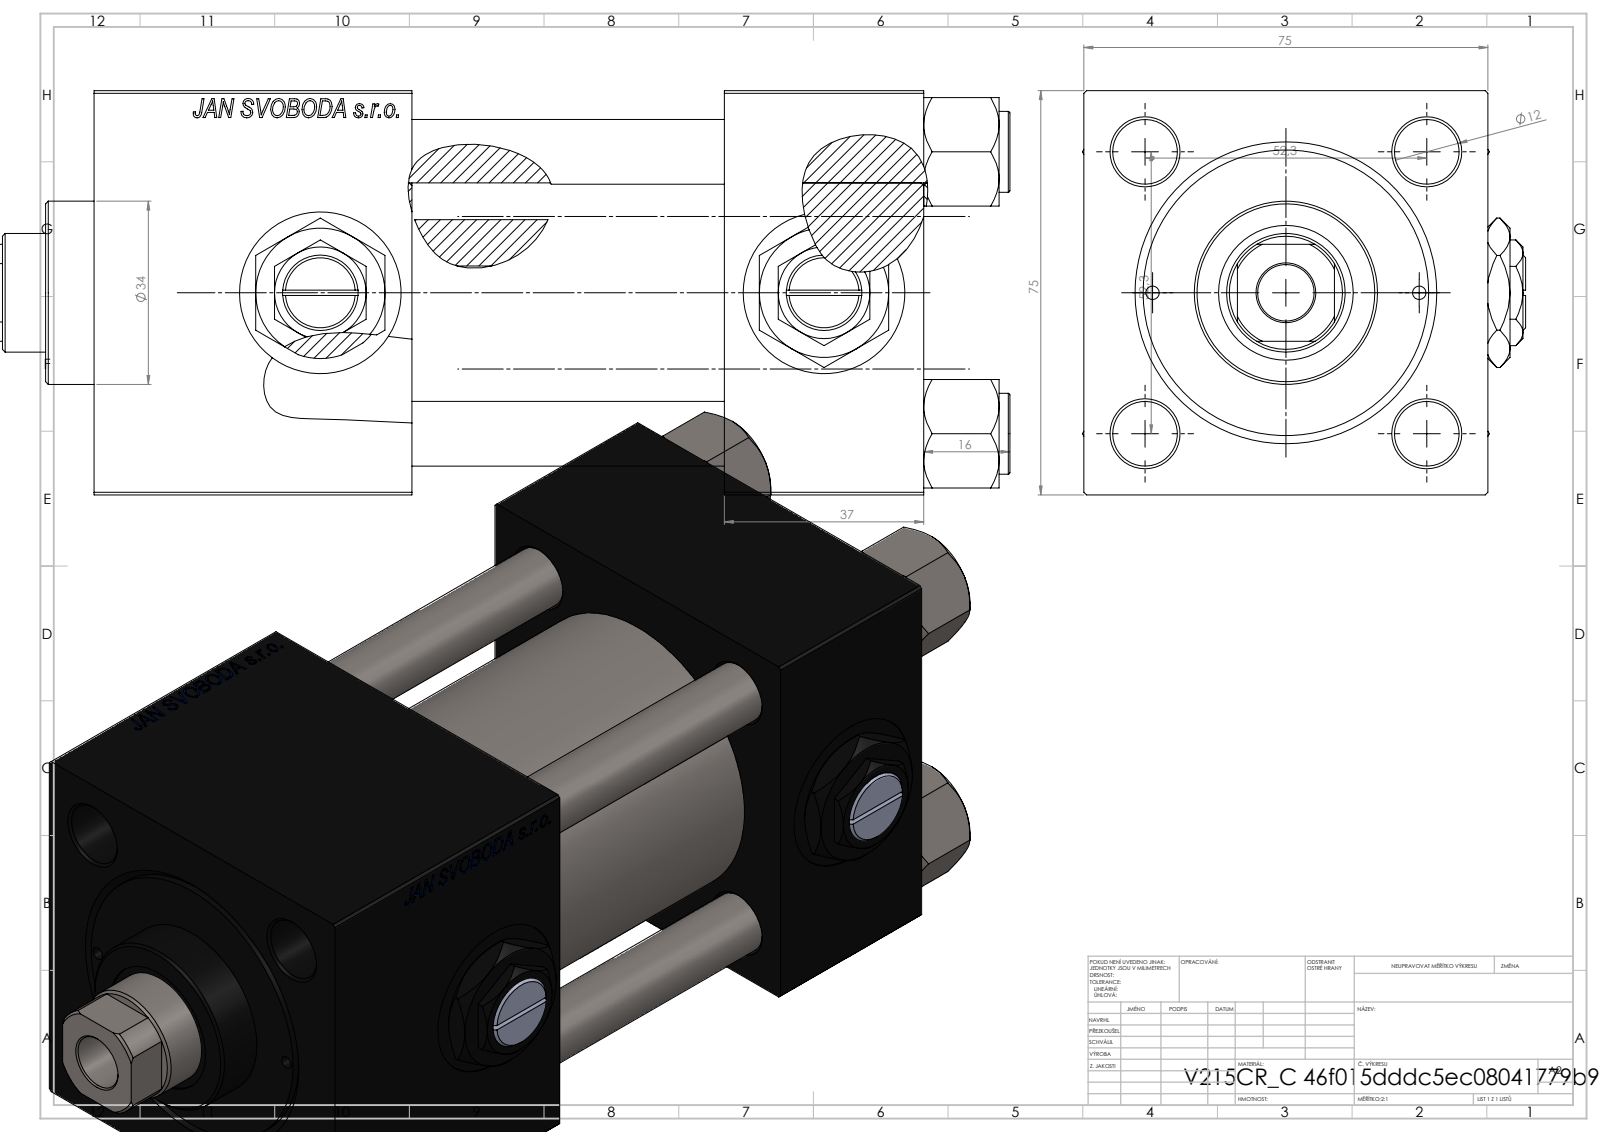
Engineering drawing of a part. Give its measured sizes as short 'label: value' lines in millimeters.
name: V215_VC_A; V215CR_C_Body; NUT_M5_C; V215CR_C_TYCINKA (+2 more)
written by: SolidWorks 2019 (CONFIG_CONTROL_DESIGN)
unit: mm
bodies: 13 solids, 1255 faces (575 planar, 102 cylindrical, 578 other)
size: 195 × 82.27 × 75
volume: 651 788 mm³; area: 151 841 mm²
holes: 4× ⌀12, 2× ⌀2.5, 2× ⌀7, 2× ⌀20.96, 2× ⌀30, 1× ⌀10.5, 1× ⌀22, 1× ⌀25, 1× ⌀41, 1× ⌀50, 1× ⌀53
bosses: 4× ⌀15, 1× ⌀56, 1× ⌀34
rounds: 1× R10.5
face distances: 75, 37, 154, 117, 95, 58, 59, 125.3, 88.3, 30.3
hole spacings: 26.19, 36.98, 52.3, 57.22, 24.75, 73.96, 49.5, 93.5
